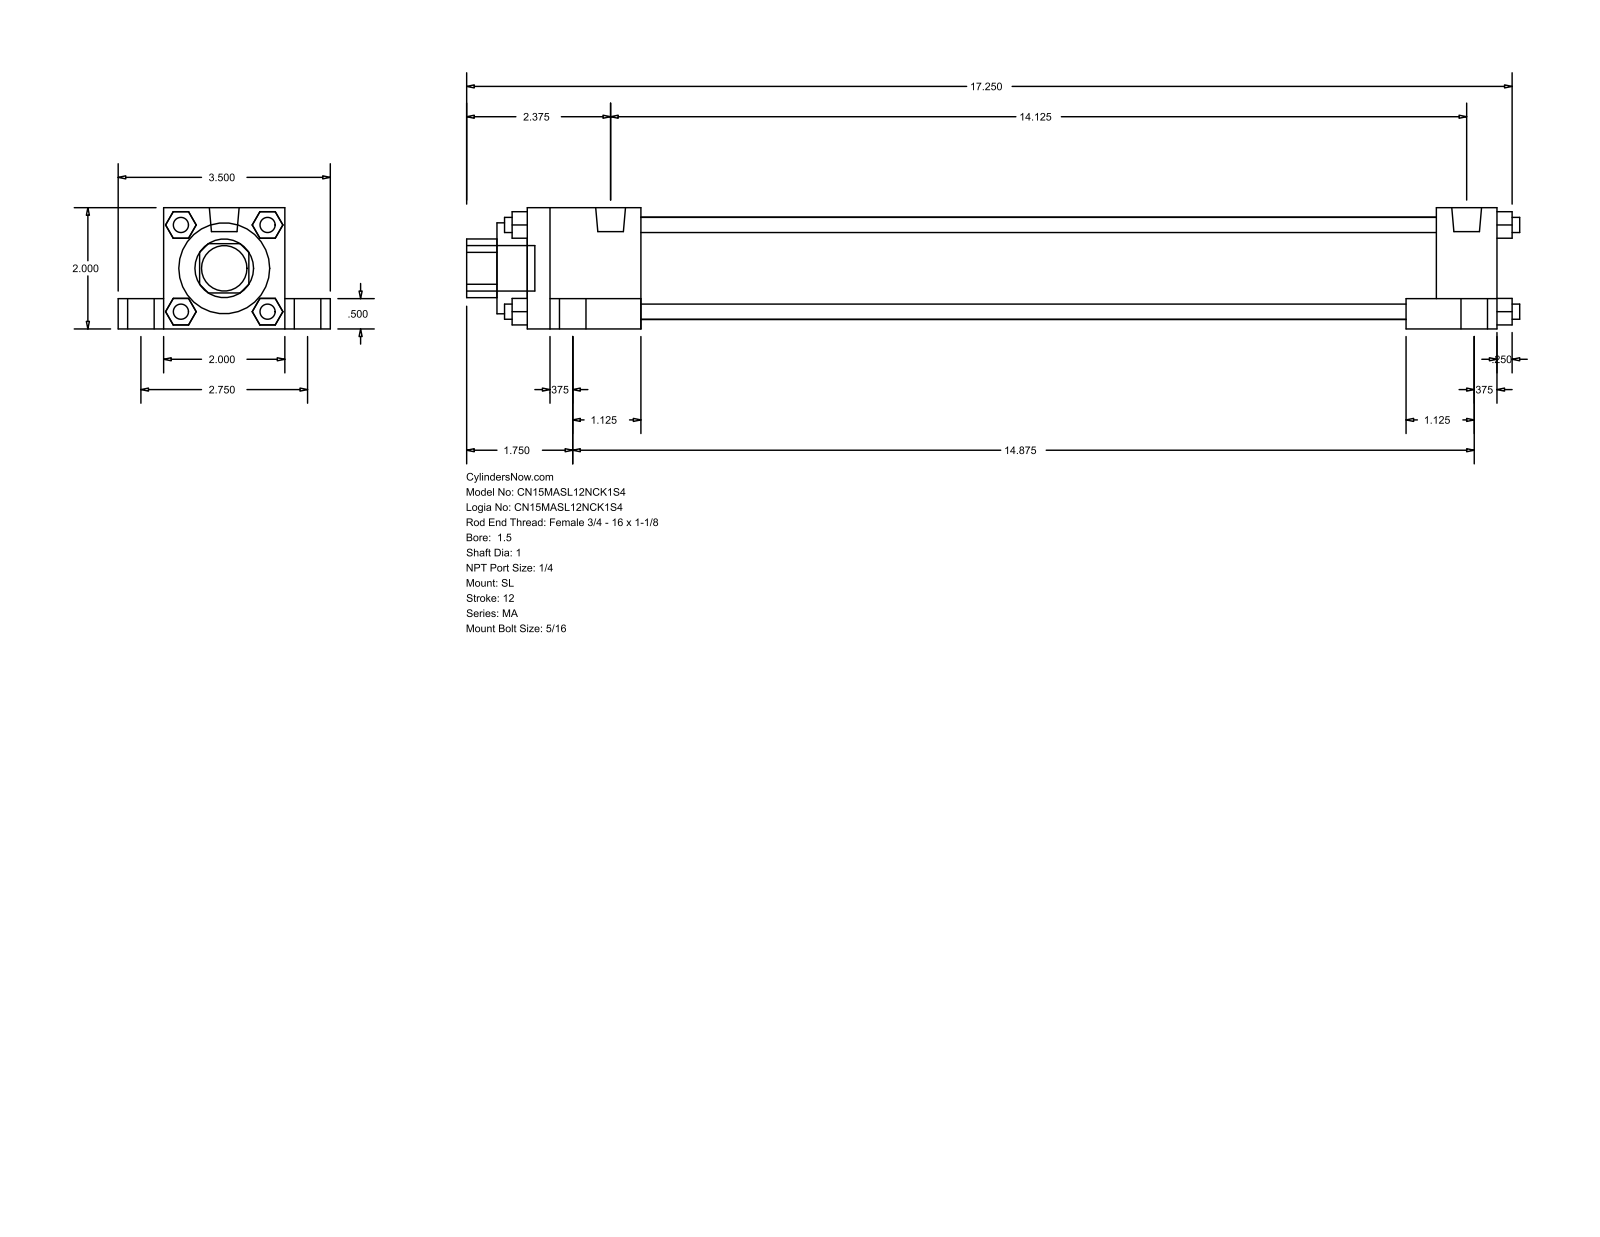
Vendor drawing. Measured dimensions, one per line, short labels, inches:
name: MA_SL__0150_1
written by: GSSL Pune (CONFIG_CONTROL_DESIGN)
unit: in
bodies: 0 solids, 148 faces (112 planar, 36 cylindrical, 0 other)
size: 17.375 × 3.5 × 2
holes: 1× ⌀1, 1× ⌀1.5, 1× ⌀1.69
bosses: 4× ⌀0.687, 4× ⌀0.437, 4× ⌀0.313, 4× ⌀0.25, 2× ⌀0.492, 1× ⌀0.75
rounds: 1× R0.484
face distances: 2, 0.5, 0.75, 0.375, 2.75, 1.5, 0.25, 16, 1, 15
